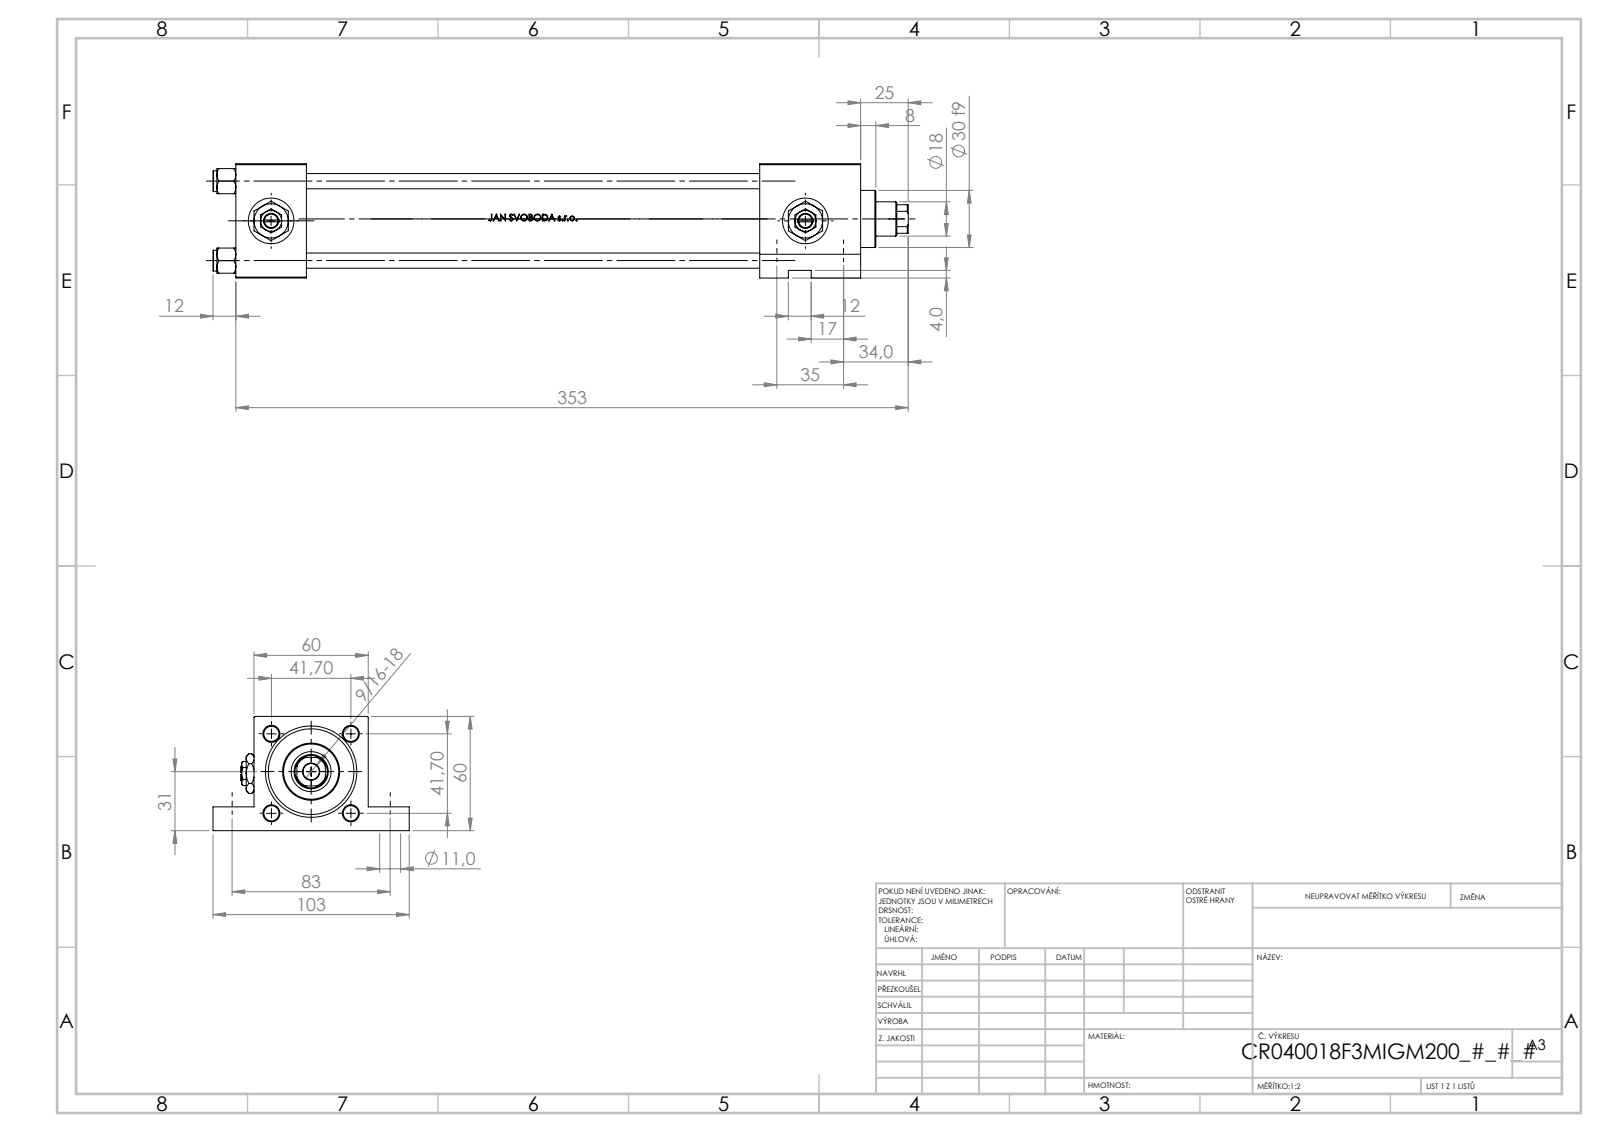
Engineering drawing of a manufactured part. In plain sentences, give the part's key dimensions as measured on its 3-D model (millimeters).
The part is named "Zatka_pro_OIL_PORT; V215CR_F_TYCINKA; NUT_M5_F; V215_VC_A (+2 more)". Its 3-D file was written by "SolidWorks 2019 (CONFIG_CONTROL_DESIGN)". It is 13 solids with 1215 faces: 484 planar, 149 cylindrical and 582 other. Overall it measures 365 by 103 by 60 millimeters. Its volume is 575 317 cubic millimeters and its surface area 191 375 square millimeters. Round holes: 4 of diameter 8, 4 of diameter 11, 3 of diameter 16.66, 3 of diameter 24, 2 of diameter 7, 1 of diameter 8.5, 1 of diameter 16, 1 of diameter 18, 1 of diameter 21, 1 of diameter 31, 1 of diameter 40, 1 of diameter 45. Round bosses or shafts: 4 of diameter 11, 1 of diameter 46, 1 of diameter 30. Partial cylindrical surfaces (rounded edges, fillets, slot ends): 1 of radius 8.5. The main face-to-face distances are 60, 37, 328, 291, 275, 238, 53, 299.3, 262.3, 24.3. The hole center spacings are 41.7, 28.79, 30.2, 35, 42.09, 50.06, 58.97, 83.
